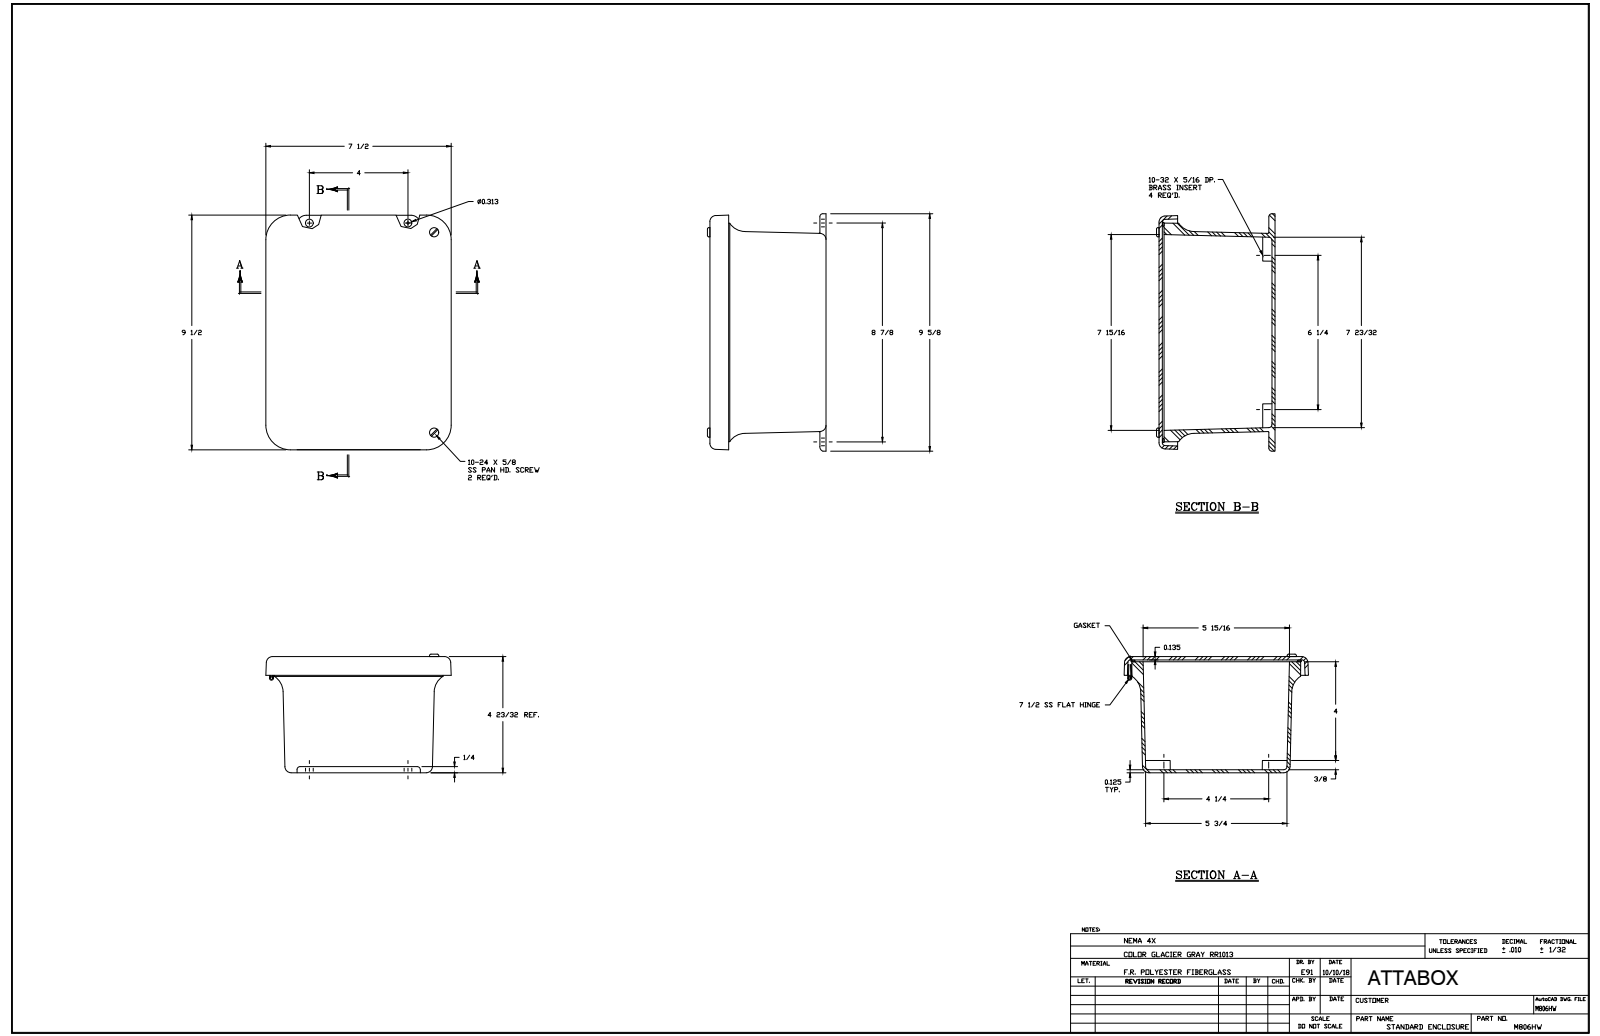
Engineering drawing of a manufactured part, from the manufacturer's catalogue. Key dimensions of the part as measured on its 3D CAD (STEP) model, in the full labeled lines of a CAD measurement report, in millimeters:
Part name (STEP PRODUCT): M806HW
STEP written by: SolidWorks 2018 (AUTOMOTIVE_DESIGN)
Units: millimetres
Bodies: 20 solids, 702 faces (228 planar, 267 cylindrical, 207 other)
Overall size (bounding box): 244.5 × 191.6 × 123.1
Volume: 739 100 mm³ · Surface area: 389 600 mm²
Round holes (diameter × count): ⌀3.3 ×6, ⌀3.6 ×6, ⌀3.9 ×5, ⌀4 ×4, ⌀5.5 ×4, ⌀3.7 ×2, ⌀2.2 ×1, ⌀2.2 ×1
Round bosses / shafts (diameter × count): ⌀6.9 ×6, ⌀6.4 ×6, ⌀3.2 ×4, ⌀4.8 ×2, ⌀4 ×2, ⌀3.2 ×2, ⌀3.9 ×1
Partial cylindrical surfaces — rounded edges, fillets, slot ends (radius × count): R0.8 ×20, R3.2 ×12, R6.4 ×8, R5.1 ×7, R9.5 ×4, R19.5 ×4, R0.8 ×2
Main face-to-face distances: 3.2, 3.4, 116.3, 119.8, 3.2, 113.2, 116.6, 114.3, 111.1, 2
Hole centre spacings: 88.9, 33.7, 133.9, 184.1, 225.1, 6.4, 82.6, 76.2
